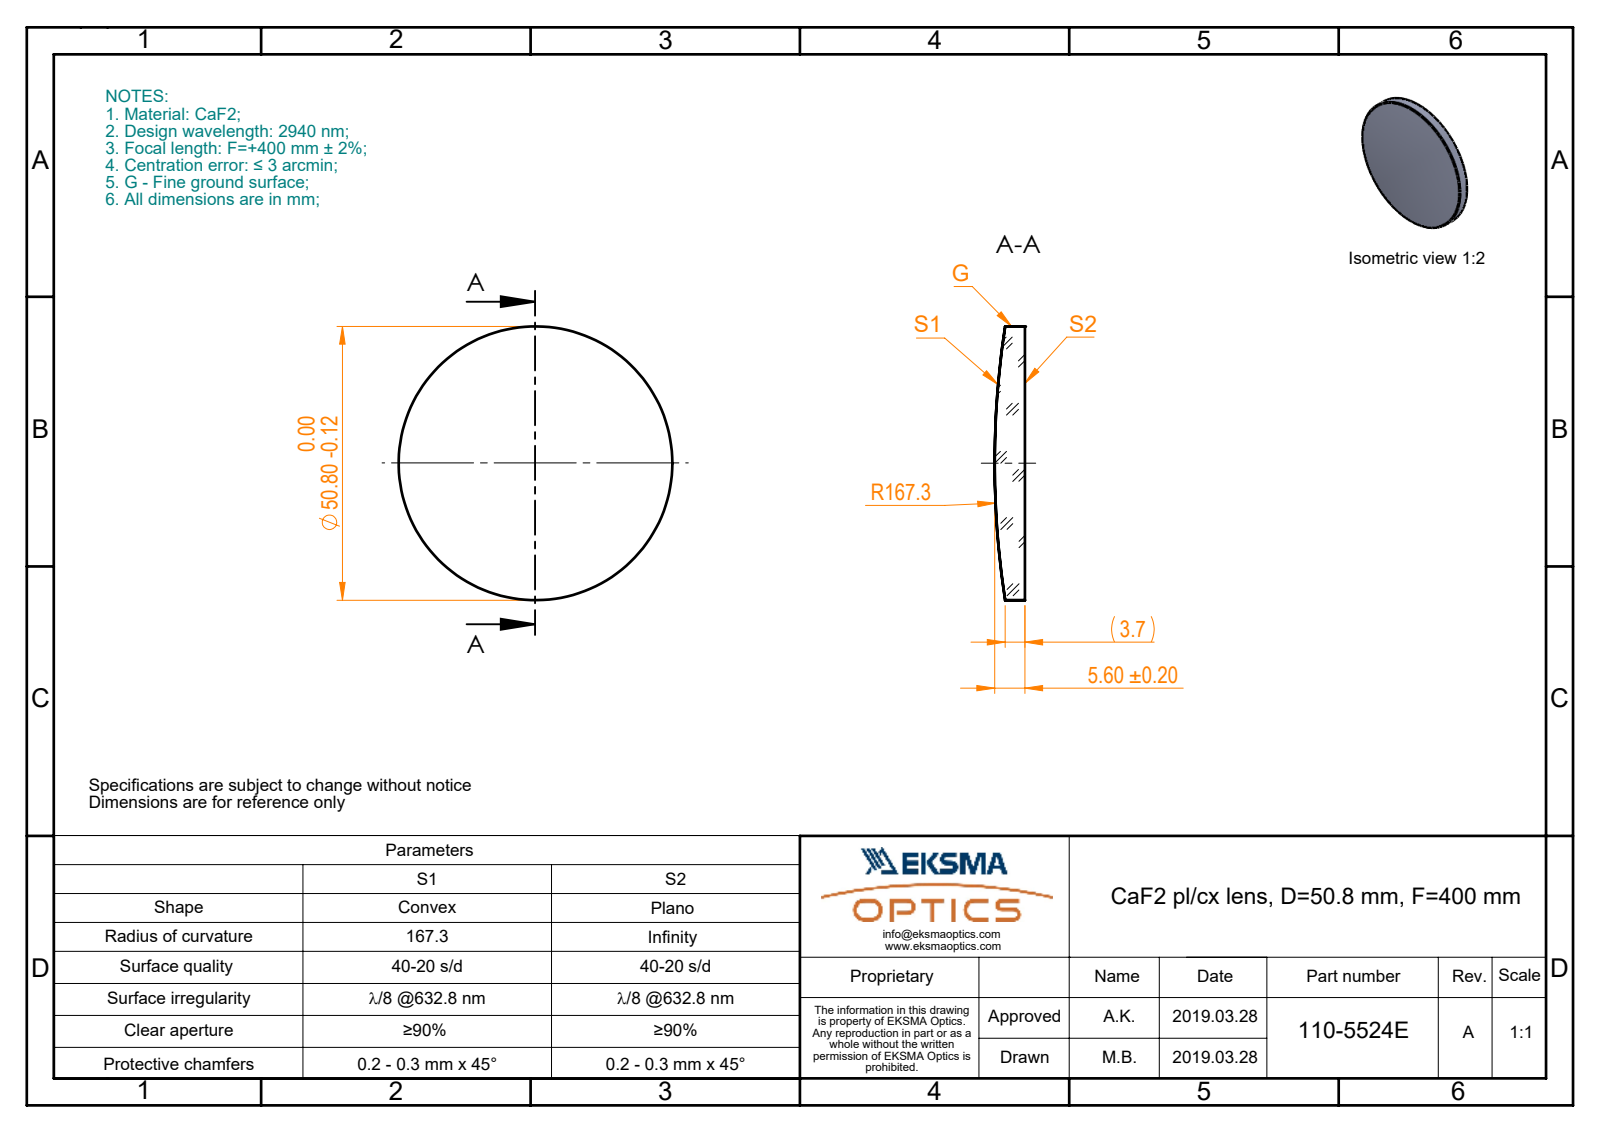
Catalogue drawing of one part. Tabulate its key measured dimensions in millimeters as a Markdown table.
| quantity | value |
| --- | --- |
| part name | 110-5524E CaF2 pl-cx 50.8 F400 |
| STEP written by | SolidWorks 2017 (CONFIG_CONTROL_DESIGN) |
| units | millimeters |
| bodies | 1 solid, 5 faces (1 planar, 2 cylindrical, 2 other) |
| overall size | 50.8 × 50.8 × 5.6 |
| volume | 9 389 mm³ |
| surface area | 4 650 mm² |
| round bosses / shafts (diameter × count) | 50.8 × 1 |
